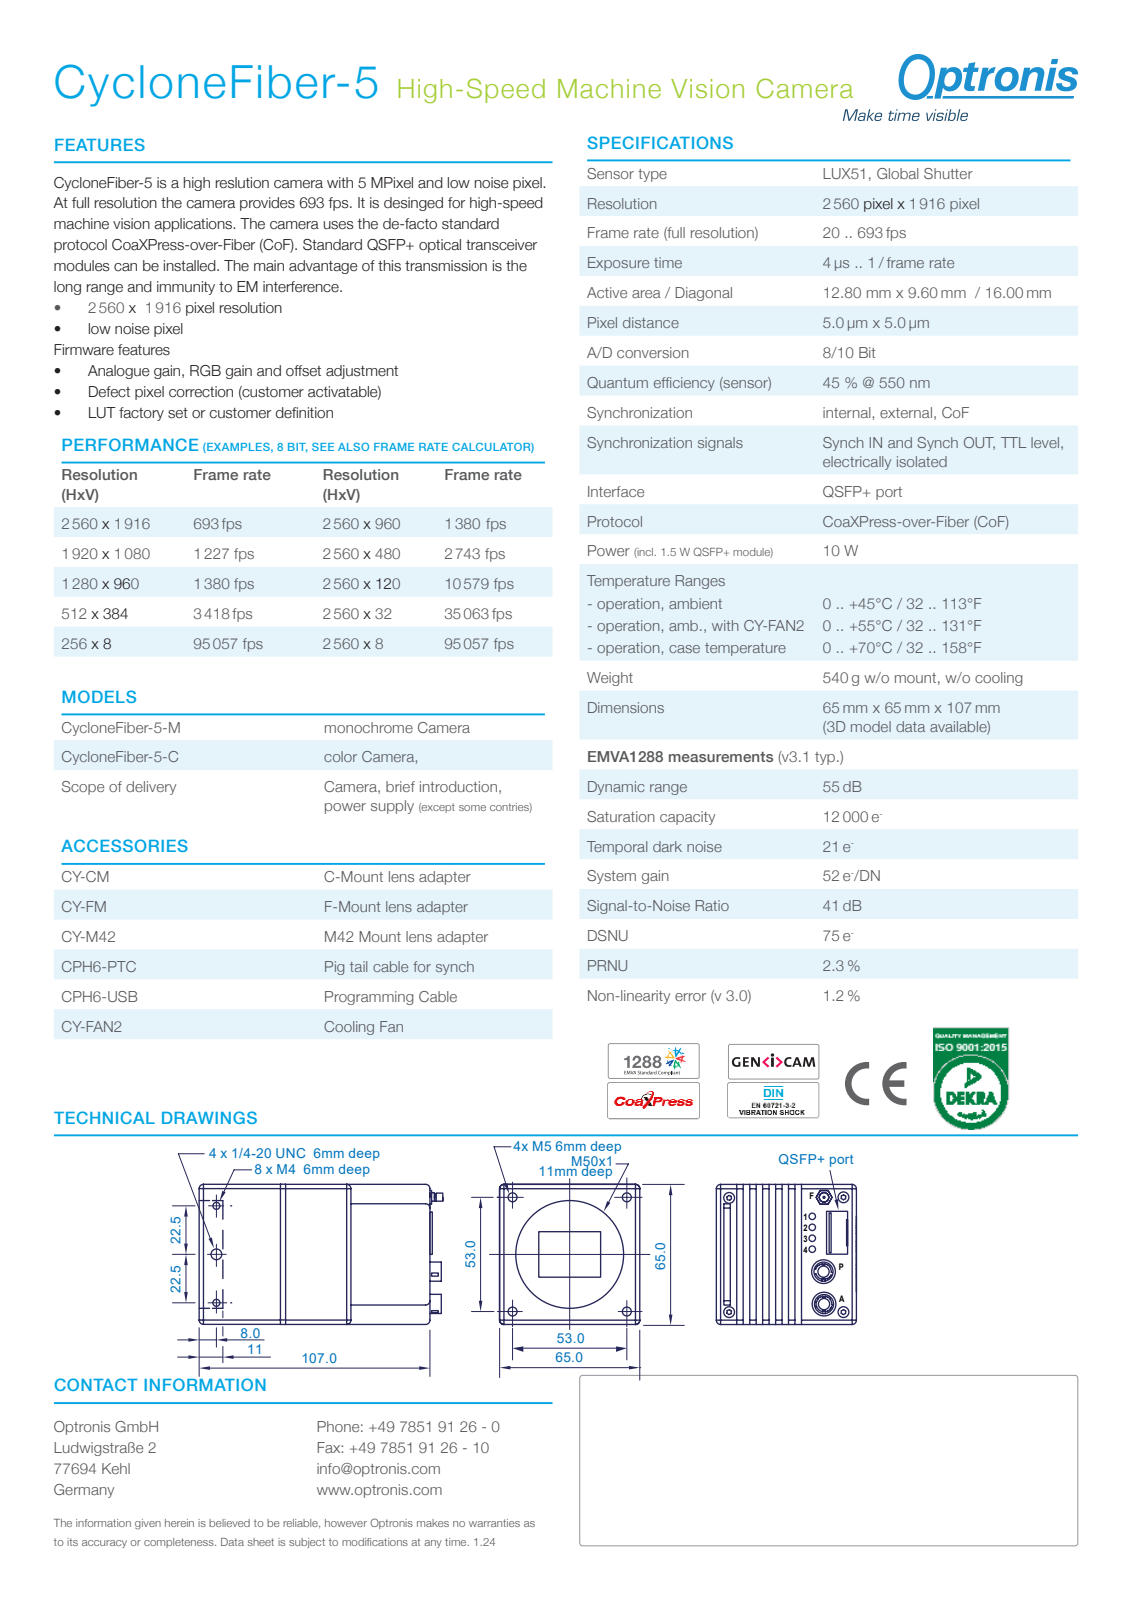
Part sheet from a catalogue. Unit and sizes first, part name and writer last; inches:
Units: inches
Overall size (bounding box): 4.232 × 2.559 × 2.559
Round holes (diameter × count): ⌀0.039 ×28, ⌀0.031 ×16, ⌀0.106 ×12, ⌀0.02 ×10, ⌀0.062 ×8, ⌀0.079 ×4, ⌀0.087 ×4, ⌀0.112 ×4, ⌀0.128 ×4, ⌀0.165 ×4, ⌀0.197 ×4, ⌀0.217 ×4
Round bosses / shafts (diameter × count): ⌀0.034 ×209, ⌀0.012 ×209, ⌀0.043 ×12, ⌀0.098 ×8, ⌀0.185 ×4, ⌀0.177 ×4, ⌀0.15 ×4, ⌀0.138 ×4
Partial cylindrical surfaces — rounded edges, fillets, slot ends (radius × count): R0.01 ×188, R0.008 ×60, R0.004 ×45, R0.02 ×44, R0.039 ×40, R0.079 ×34, R0.005 ×28, R0.118 ×28
Main face-to-face distances: 0.118, 0.236, 0.354, 0.472, 0.591, 0.709, 0.827, 0.945, 0.079, 1.063
Hole centre spacings: 0.132, 0.308, 0.265, 0.197, 0.5, 0.283, 0.432, 0.177
Volume: 8.139 in³ · Surface area: 175.3 in²
Bodies: 5 solids, 5005 faces (2627 planar, 2112 cylindrical, 266 other)
Part name (STEP PRODUCT): 1200-MG-13_CycloneFiber_short
STEP written by: Autodesk Inventor 2026 (AUTOMOTIVE_DESIGN)
